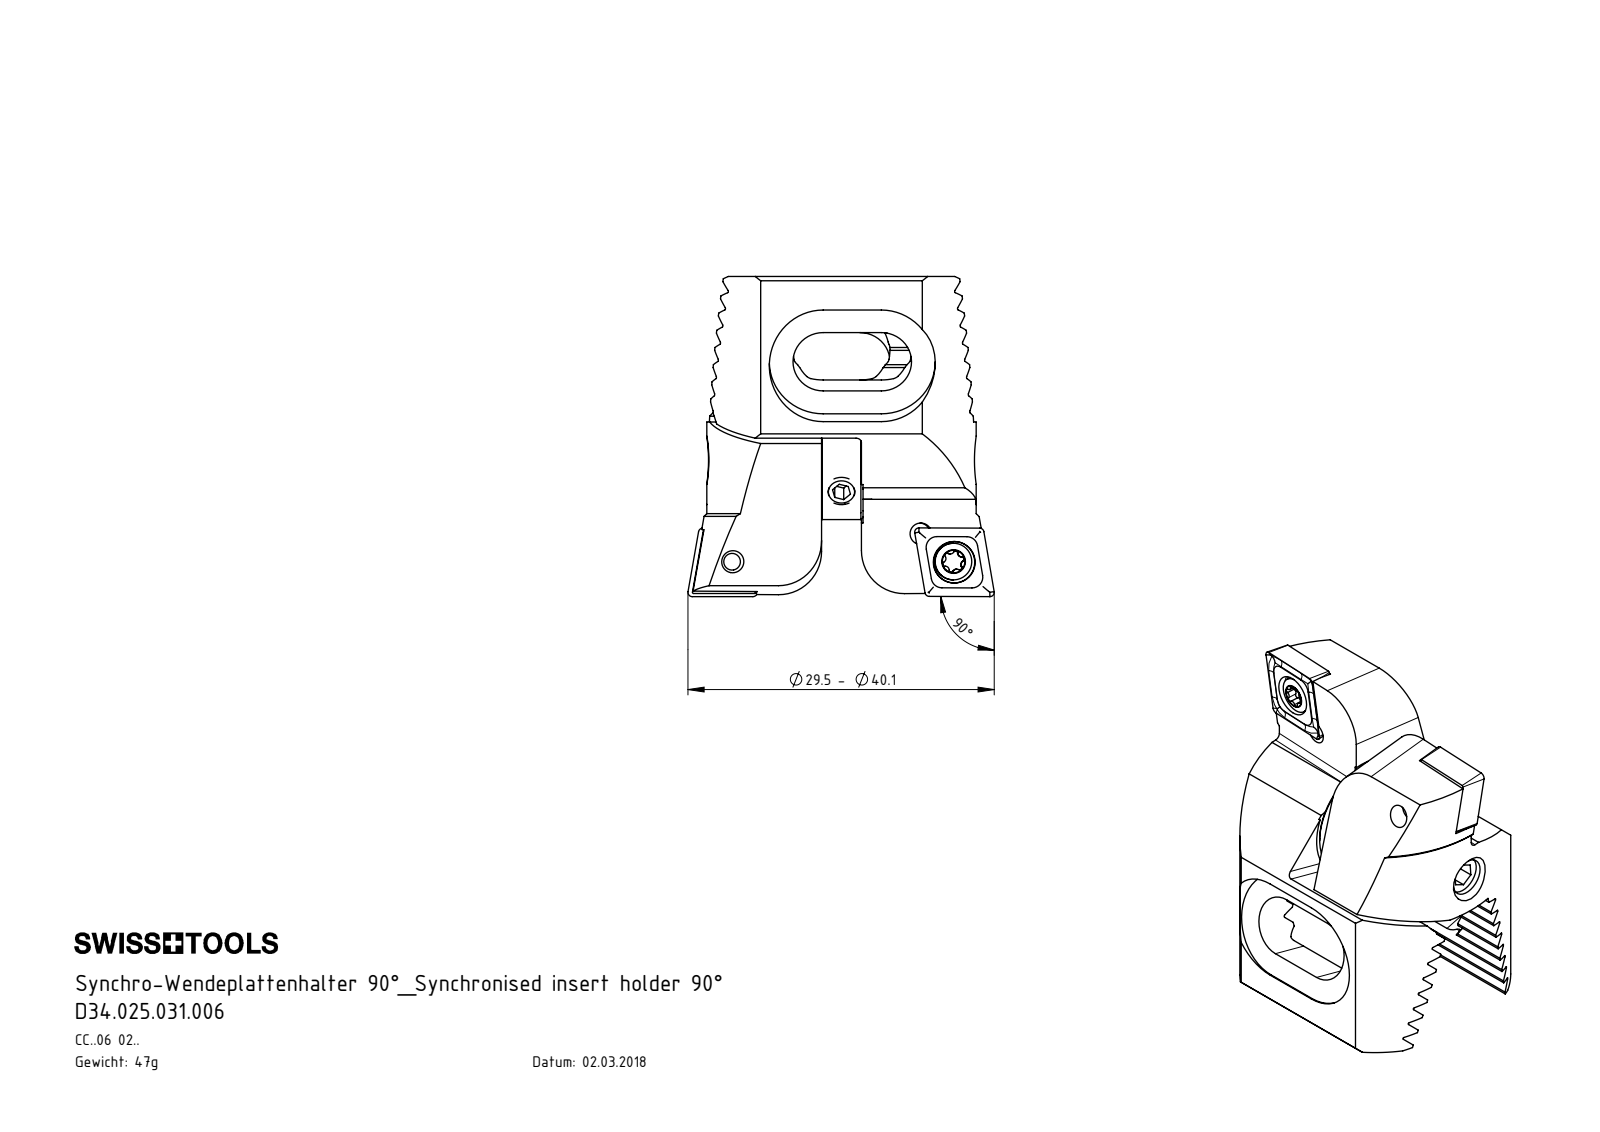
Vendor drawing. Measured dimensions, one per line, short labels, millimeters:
name: Z25-WCA.001.016_A; D34.025.031.006; Z25-ER3.002.004_B; Z25-ER3.001.023_A (+4 more)
written by: SolidWorks 2017 (CONFIG_CONTROL_DESIGN)
unit: mm
bodies: 11 solids, 517 faces (205 planar, 172 cylindrical, 140 other)
size: 29.7 × 28.43 × 20.2
volume: 5 848 mm³; area: 5 400 mm²
holes: 3× ⌀1, 3× ⌀2.5, 2× ⌀2, 2× ⌀2.05, 2× ⌀2.8, 2× ⌀3.85, 1× ⌀3.5
bosses: 4× ⌀3, 2× ⌀3.4, 2× ⌀2.5, 1× ⌀11, 1× ⌀4
rounds: 16× R0.12, 12× R0.21, 10× R0.36, 8× R1, 4× R0.5, 4× R2.8, 4× R5, 2× R0.36
face distances: 1.43, 2.86, 4.29, 5.72, 3.14, 7.14, 8.57, 7.15, 4, 5.71
hole spacings: 2, 3.98, 3.99, 4.08, 4.09, 7.19, 7.2, 7.47
